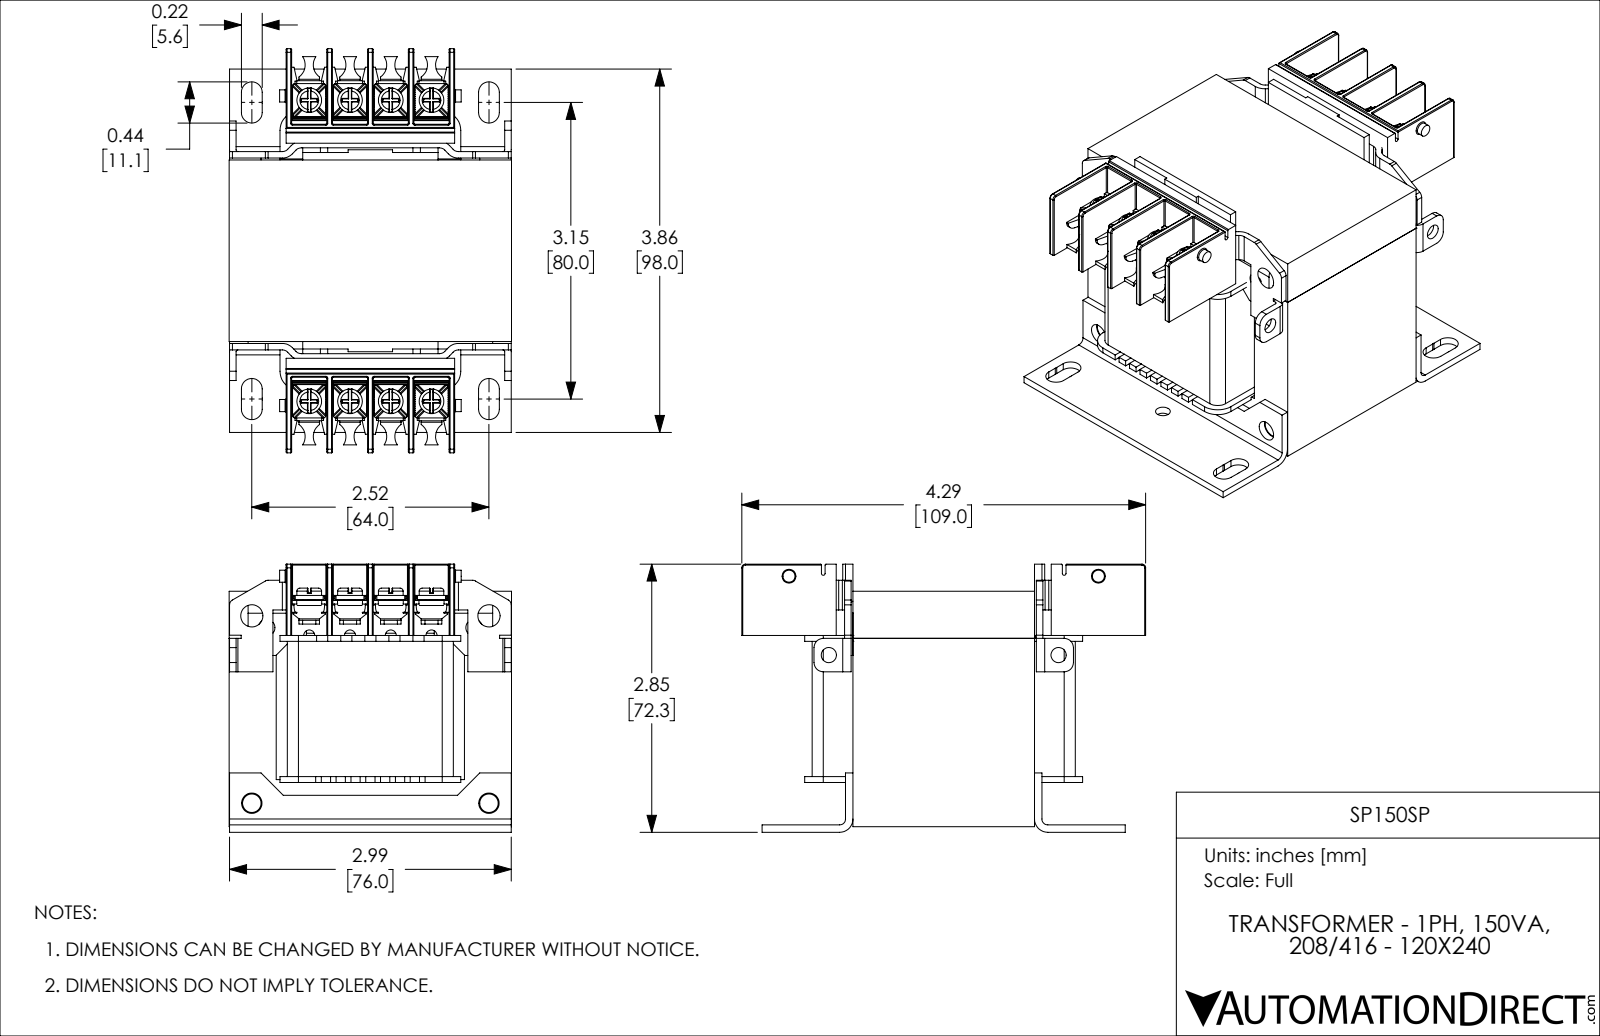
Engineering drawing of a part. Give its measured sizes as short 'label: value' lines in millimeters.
name: SP150SP
written by: SolidWorks 2018 (AUTOMOTIVE_DESIGN)
unit: mm
bodies: 42 solids, 3183 faces (1948 planar, 941 cylindrical, 294 other)
size: 109 × 76.2 × 72.3
volume: 301 800 mm³; area: 107 100 mm²
holes: 10× ⌀4, 8× ⌀2.7, 8× ⌀3.5, 2× ⌀2.5, 2× ⌀4.1, 2× ⌀4.5, 2× ⌀5, 2× ⌀5.5, 2× ⌀6
bosses: 8× ⌀6.7, 8× ⌀6.1, 8× ⌀4.3, 8× ⌀2.8, 3× ⌀3.3
rounds: 52× R0.1, 52× R0.3, 46× R0.3, 32× R0.7, 18× R1.5, 16× R4, 12× R0.9, 10× R2
face distances: 12.7, 50.8, 1.5, 11, 2, 63.5, 60.5, 25.4, 49, 38.1
hole spacings: 11, 22, 81.7, 33, 80.9, 83.9, 81.5, 81.9
